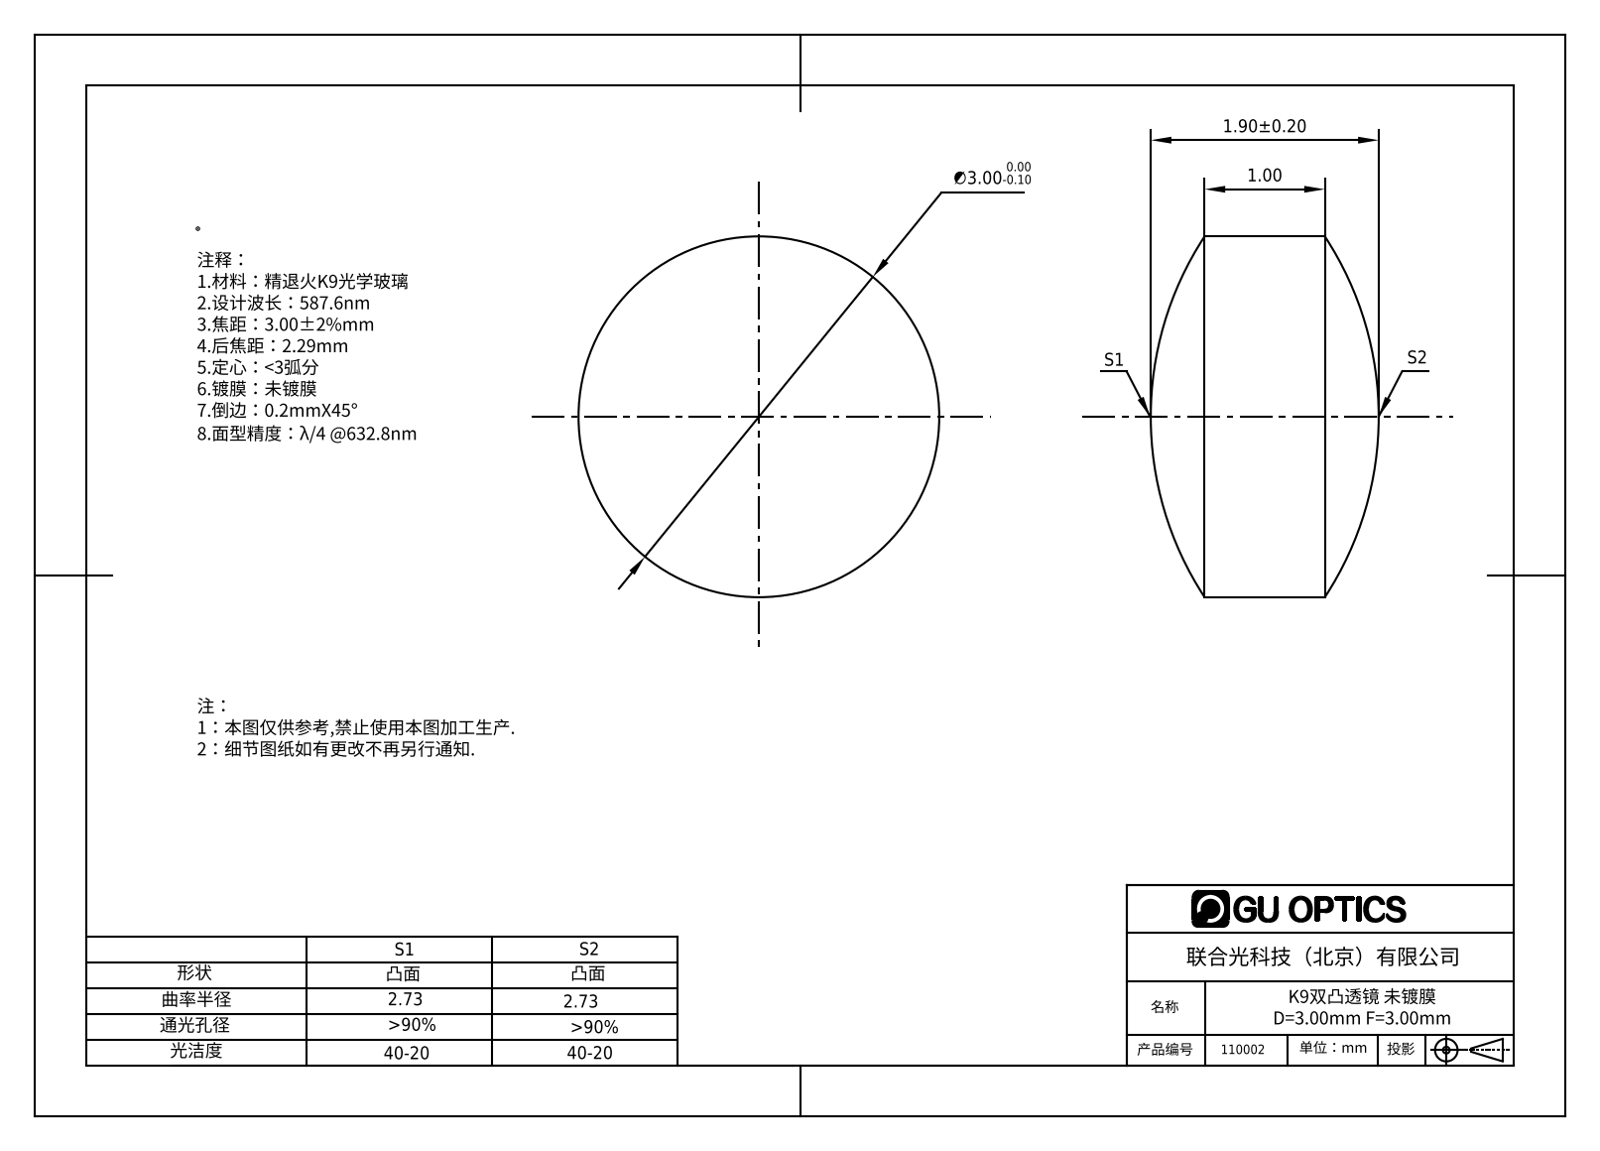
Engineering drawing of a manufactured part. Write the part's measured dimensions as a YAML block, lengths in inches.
part_name: "110002"
step_written_by: "SolidWorks 2020 (CONFIG_CONTROL_DESIGN)"
units: inches
bodies: {solids: 1, faces: 6, planar: 0, cylindrical: 2, other: 4}
overall_size: [0.118, 0.118, 0.075]
volume: 0.001
surface_area: 0.039
round_bosses_or_shafts:
  - {diameter: 0.118, count: 1}
